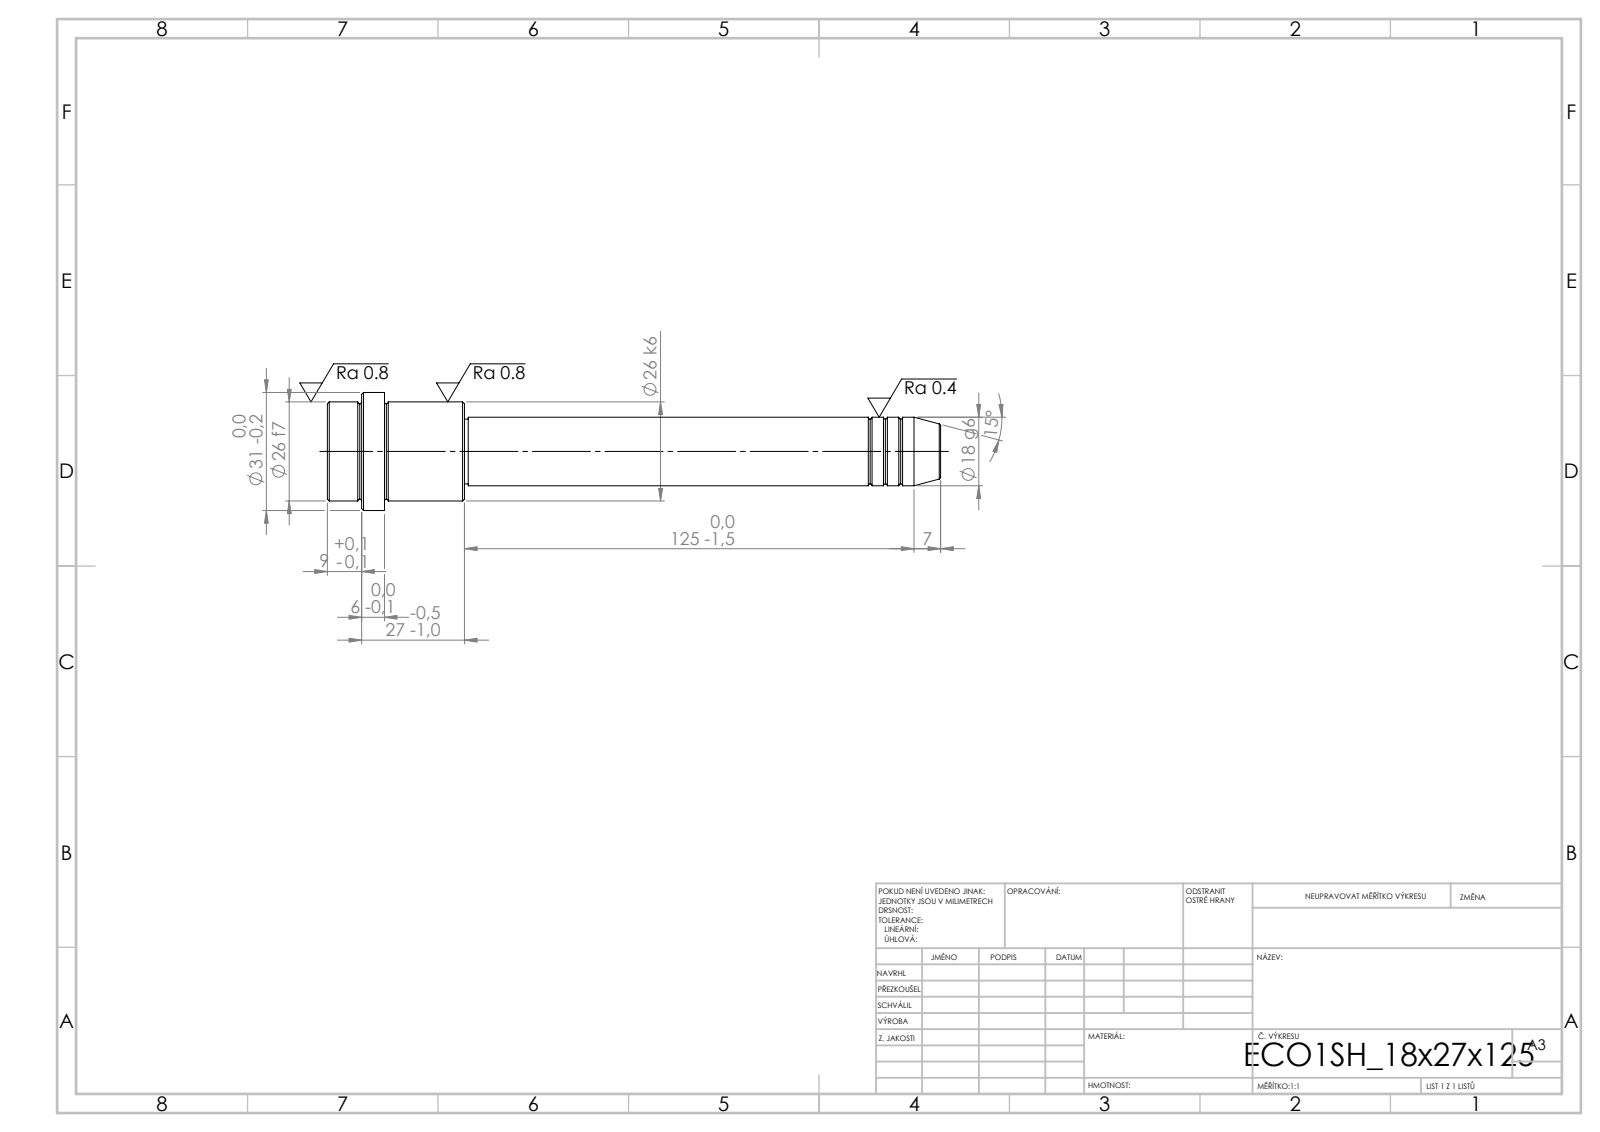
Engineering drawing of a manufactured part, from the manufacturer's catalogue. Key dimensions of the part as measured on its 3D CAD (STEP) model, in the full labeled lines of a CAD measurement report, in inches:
STEP written by: SolidWorks 2019 (CONFIG_CONTROL_DESIGN)
Units: inches
Bodies: 1 solid, 52 faces (6 planar, 16 cylindrical, 30 other)
Overall size (bounding box): 6.339 × 1.22 × 1.22
Volume: 3.157 in³ · Surface area: 18.03 in²
Round bosses / shafts (diameter × count): ⌀1.22 ×1, ⌀1.024 ×1, ⌀0.709 ×1, ⌀0.669 ×1
Main face-to-face distances: 1.417, 0.827, 0.591, 1.063, 0.236, 0.354, 4.921, 5.748, 5.984, 6.339
